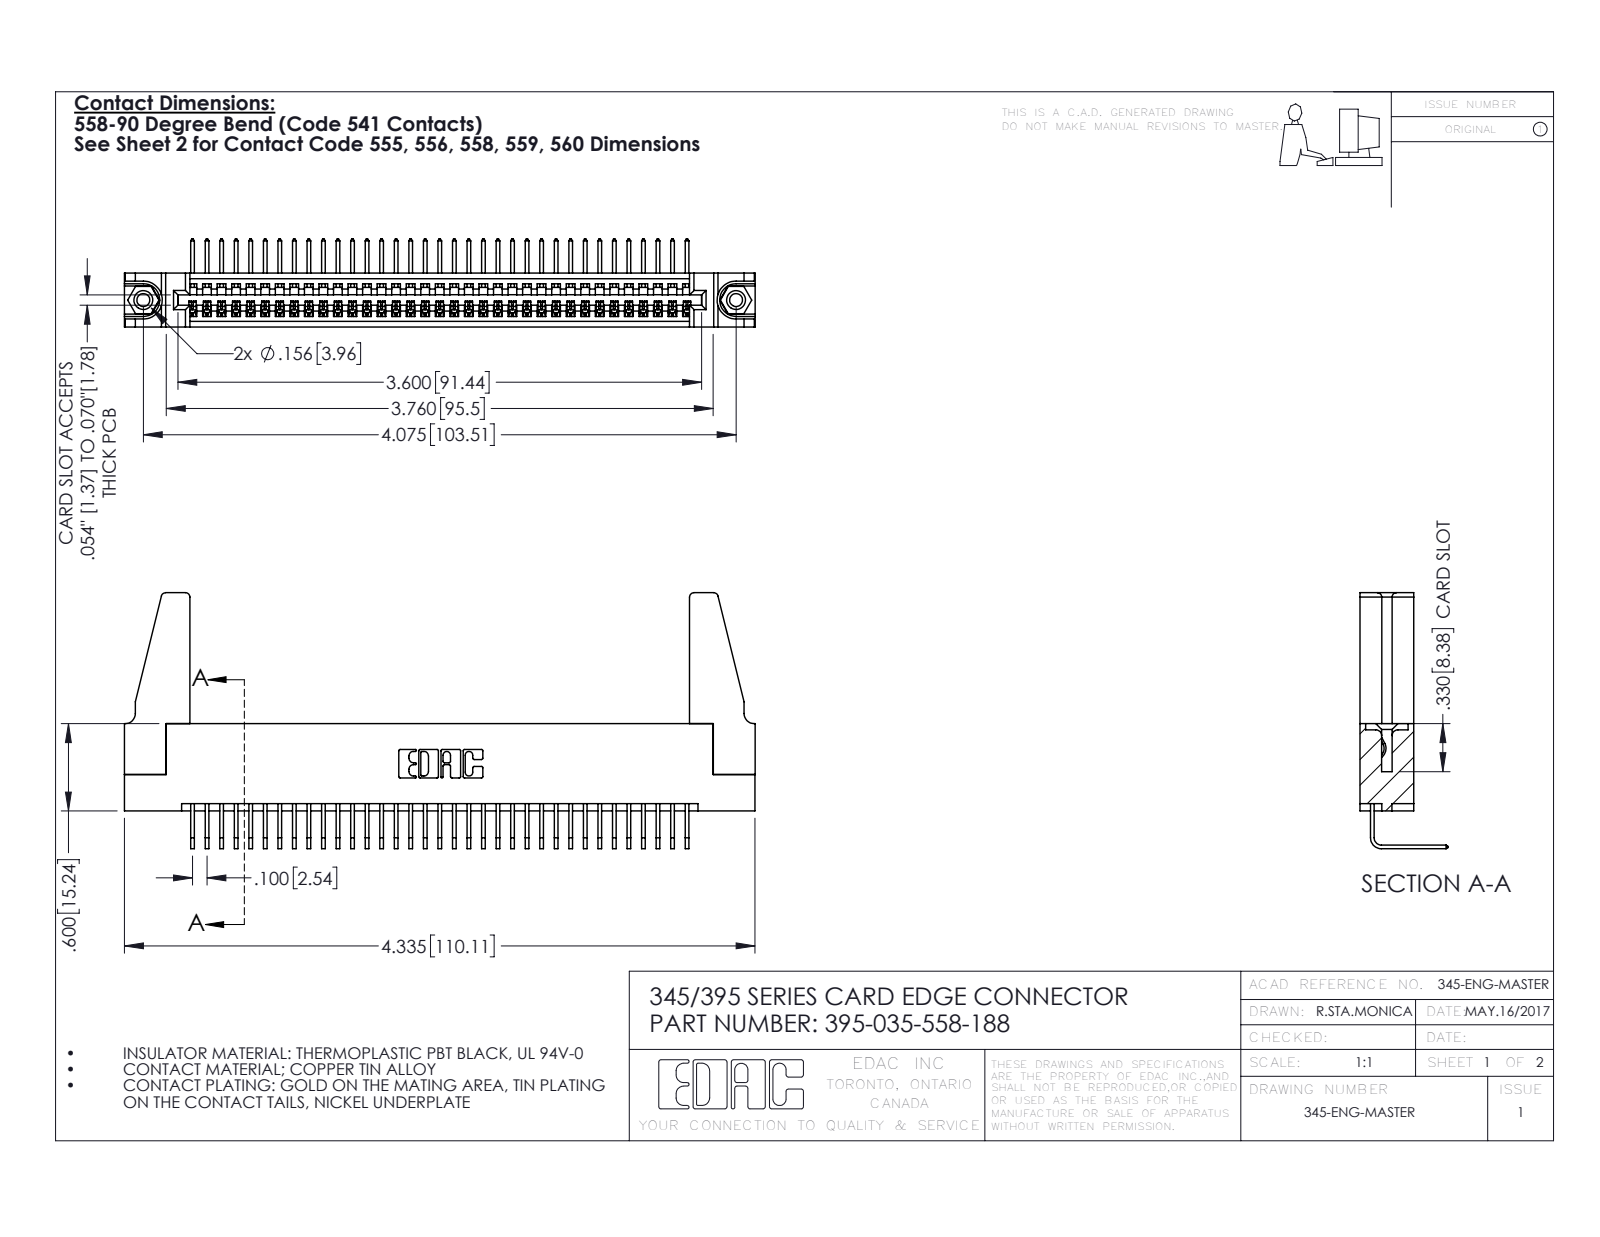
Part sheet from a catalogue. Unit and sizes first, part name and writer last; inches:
Units: inches
Overall size (bounding box): 4.336 × 1.759 × 0.605
Round holes (diameter × count): ⌀0.089 ×2, ⌀0.125 ×2, ⌀0.156 ×2, ⌀0.064 ×1
Round bosses / shafts (diameter × count): ⌀0.155 ×2
Partial cylindrical surfaces — rounded edges, fillets, slot ends (radius × count): R0.006 ×70, R0.01 ×22, R0.03 ×8, R0.007 ×6, R0.031 ×6, R0.026 ×3, R0.031 ×2, R0.04 ×2
Main face-to-face distances: 0.072, 0.298, 0.37, 0.2, 0.098, 0.272, 0.025, 0.225, 0.149, 0.072
Hole centre spacings: 0.27, 3.839, 4.075
Volume: 0.84 in³ · Surface area: 27.43 in²
Bodies: 40 solids, 2350 faces (1622 planar, 712 cylindrical, 16 other)
Part name (STEP PRODUCT): 345-292-001_558 Tail - 2; 395-035-558-188; 345-250-001_345-250-001-102; 345 Part_Flush Mounting Lugs - 0.156 Dia-TH (+1 more)
STEP written by: SolidWorks 2016 (CONFIG_CONTROL_DESIGN)
